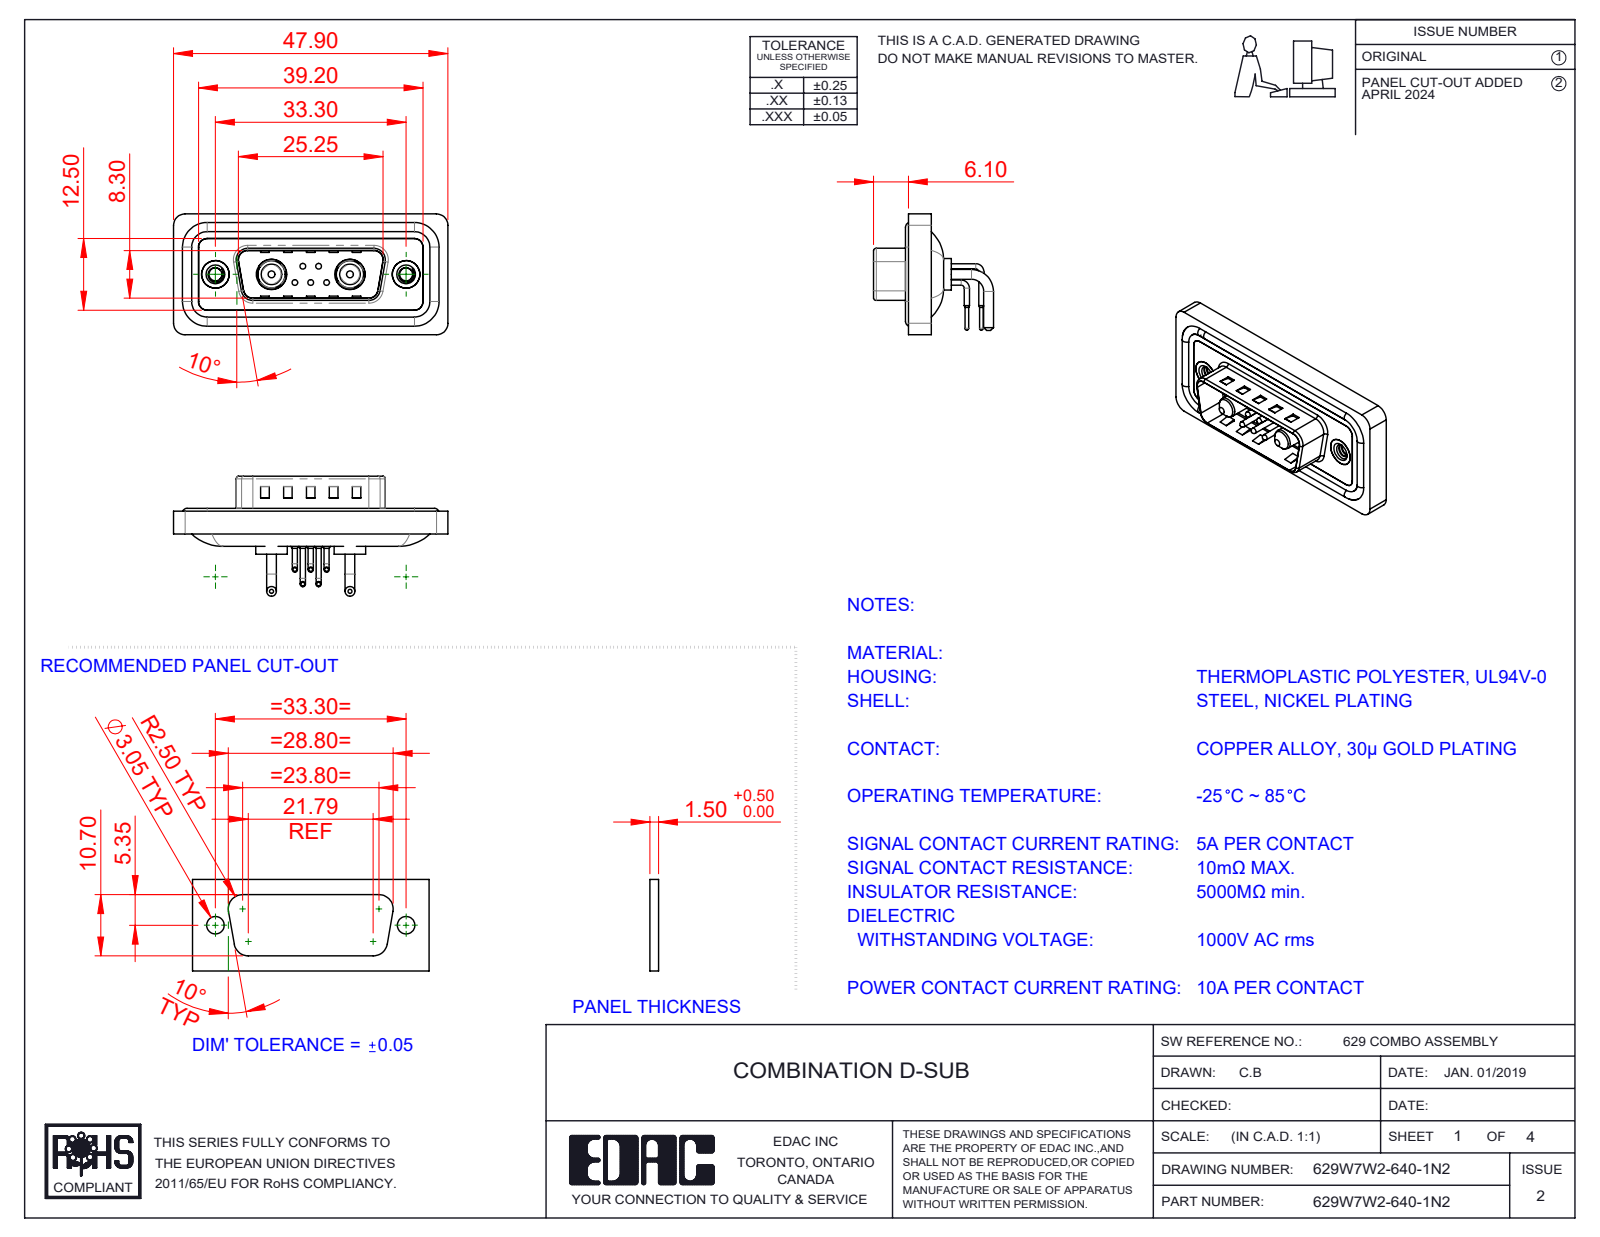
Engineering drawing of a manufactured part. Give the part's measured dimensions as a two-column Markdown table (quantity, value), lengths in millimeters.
| quantity | value |
| --- | --- |
| part name | 629Combo Housing_7W2; 629Combo Shell Front_15 Contacts; 629Combo Waterproof Housing_15 Contacts; 629Combo Threaded Rivet_2 (+5 more) |
| STEP written by | SolidWorks 2023 (CONFIG_CONTROL_DESIGN) |
| units | millimeters |
| bodies | 16 solids, 1083 faces (517 planar, 406 cylindrical, 160 other) |
| overall size | 47.9 × 21.1 × 20.95 |
| volume | 5 575 mm³ |
| surface area | 9 039 mm² |
| round holes (diameter × count) | 0.75 × 5, 1.6 × 5, 2 × 5, 2.26 × 2, 4 × 2, 4.8 × 2, 4.85 × 2, 5 × 2, 5.3 × 2 |
| round bosses / shafts (diameter × count) | 0.9 × 10, 1.5 × 5, 1 × 5, 0.65 × 5, 1.7 × 4, 1.6 × 4, 5.5 × 2, 5.2 × 2 |
| partial cylindrical surfaces (radius × count) | 2 × 20, 1.5 × 18, 0.5 × 8, 1.6 × 8, 1.01 × 5, 0.25 × 4, 0.6 × 4, 0.65 × 4 |
| main face-to-face distances | 0.4, 2.9, 0.8, 1.1, 2.1, 1.6, 2.5, 3.1, 4.5, 4.1 |
| hole center spacings | 3.16, 2.77, 9.8, 23.5, 4.31, 4.33, 5.03, 5.04 |
